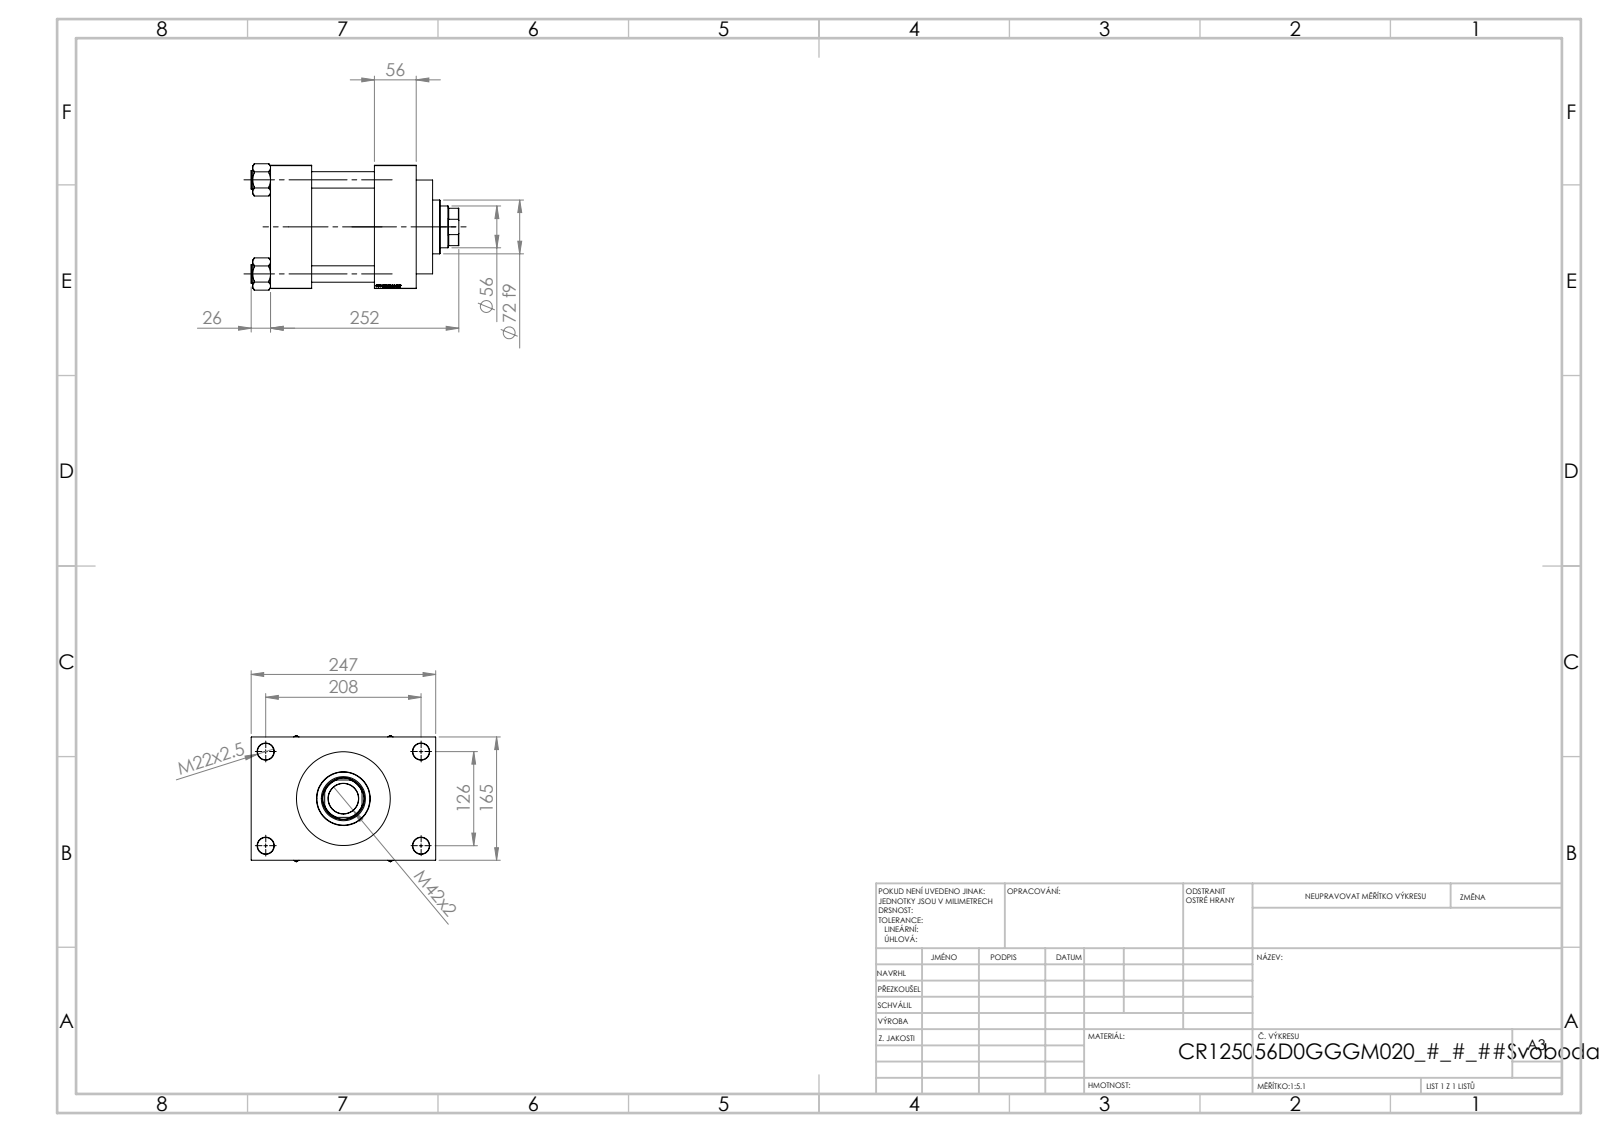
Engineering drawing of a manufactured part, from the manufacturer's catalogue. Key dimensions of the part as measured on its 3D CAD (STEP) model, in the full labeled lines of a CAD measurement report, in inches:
Part name (STEP PRODUCT): NUT_M5_D; V215CR_D_TYCINKA; V215CR_D_Body; V215_VC_A (+1 more)
STEP written by: SolidWorks 2019 (CONFIG_CONTROL_DESIGN)
Units: inches
Bodies: 11 solids, 1149 faces (544 planar, 87 cylindrical, 518 other)
Overall size (bounding box): 10.945 × 9.724 × 6.659
Volume: 302.6 in³ · Surface area: 821.4 in²
Round holes (diameter × count): ⌀0.866 ×8, ⌀0.276 ×2, ⌀1.269 ×2, ⌀1.772 ×2, ⌀1.594 ×1, ⌀2.205 ×1, ⌀2.323 ×1, ⌀3.78 ×1, ⌀4.921 ×1, ⌀4.941 ×1
Round bosses / shafts (diameter × count): ⌀0.984 ×4, ⌀5.157 ×1, ⌀2.835 ×1
Partial cylindrical surfaces — rounded edges, fillets, slot ends (radius × count): R1.063 ×1
Main face-to-face distances: 6.496, 3.307, 2.165, 5.472, 2.205, 7.677, 5.512, 1.614, 8.11, 6.84
Hole centre spacings: 1.616, 3.505, 4.787, 4.957, 5.215, 6.573, 8.233, 4.961
